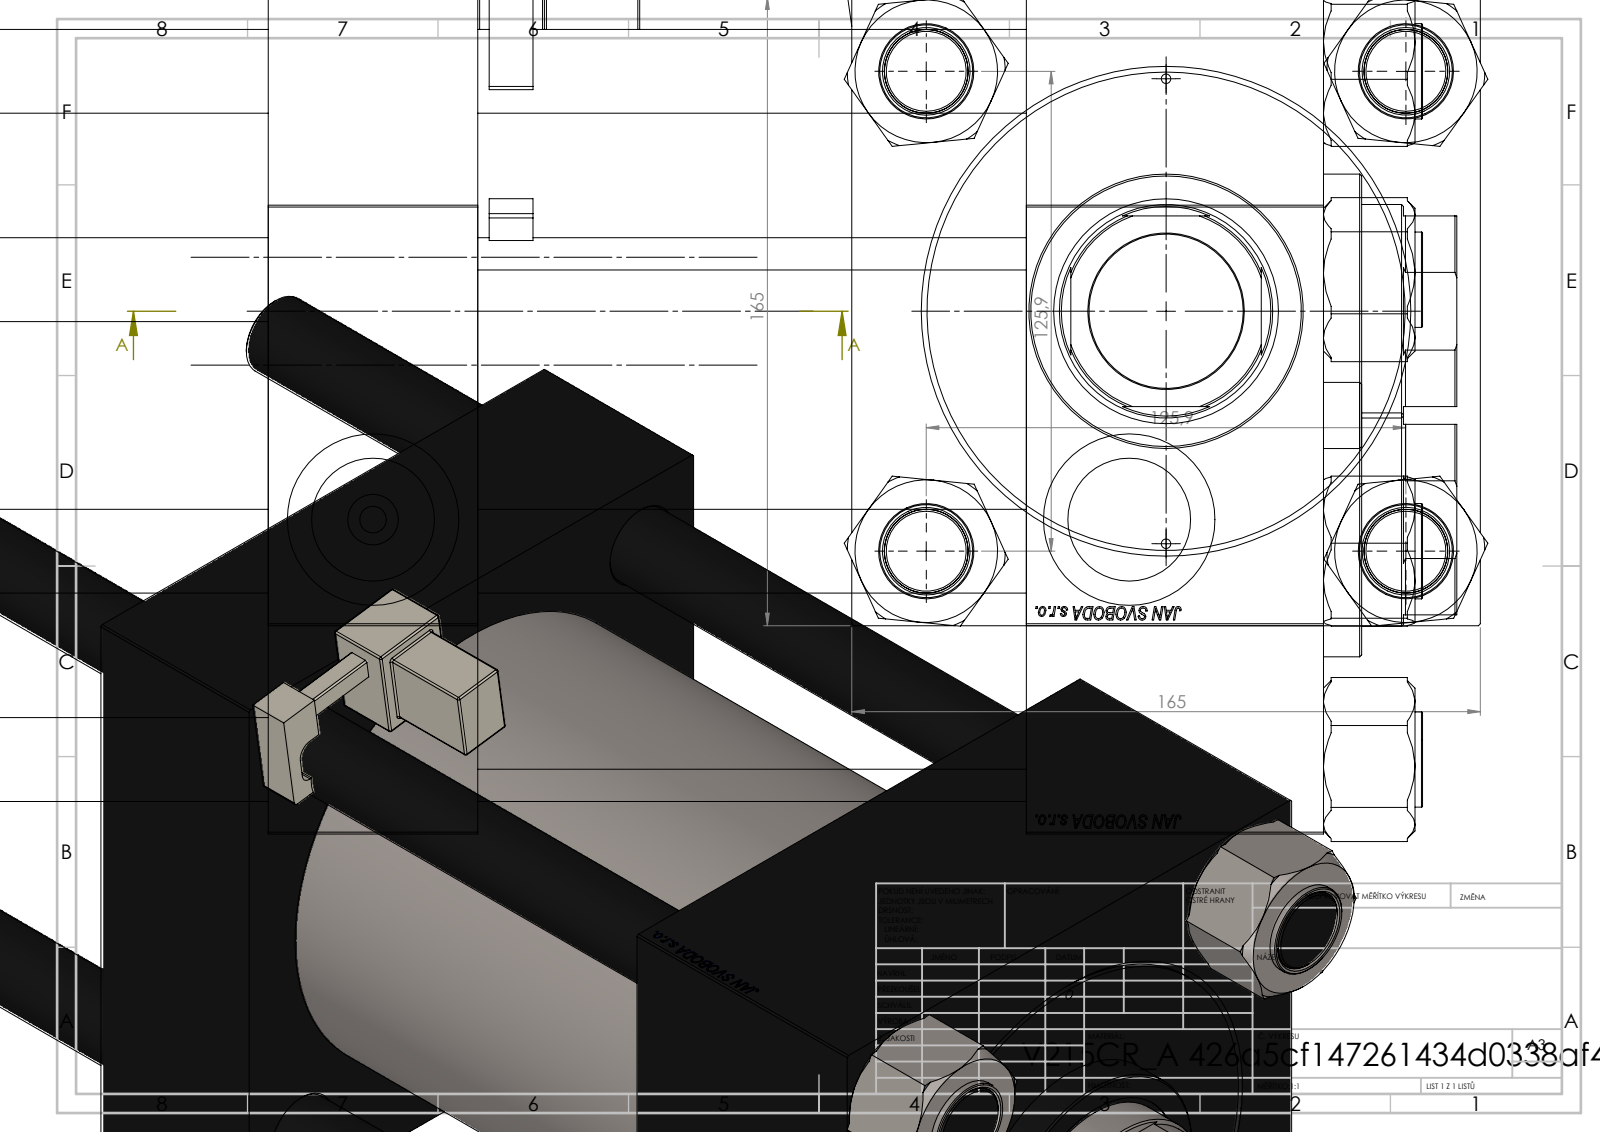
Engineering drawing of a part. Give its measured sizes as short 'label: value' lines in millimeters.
name: V215_VC_A; CR025_012_A_0_G_A_G_M_020_+#_##_TYCINKA; V215CR_MSU; V215CR_VCP (+2 more)
written by: SolidWorks 2019 (CONFIG_CONTROL_DESIGN)
unit: mm
bodies: 12 solids, 1265 faces (599 planar, 112 cylindrical, 554 other)
size: 393 × 178.03 × 168.94
volume: 5 013 000 mm³; area: 630 488 mm²
holes: 4× ⌀22, 2× ⌀2.5, 2× ⌀7, 2× ⌀32.24, 2× ⌀45, 1× ⌀40.5, 1× ⌀56, 1× ⌀59, 1× ⌀96, 1× ⌀125, 1× ⌀125.5
bosses: 4× ⌀25, 1× ⌀131, 1× ⌀72, 1× ⌀6
rounds: 24× R0.5, 1× R1, 1× R2.5, 1× R4, 1× R27
face distances: 165, 55, 277, 222, 199, 144, 78, 248.3, 193.3, 49.3
hole spacings: 62.98, 89.02, 125.9, 139.02, 61, 178.05, 122, 198.5
